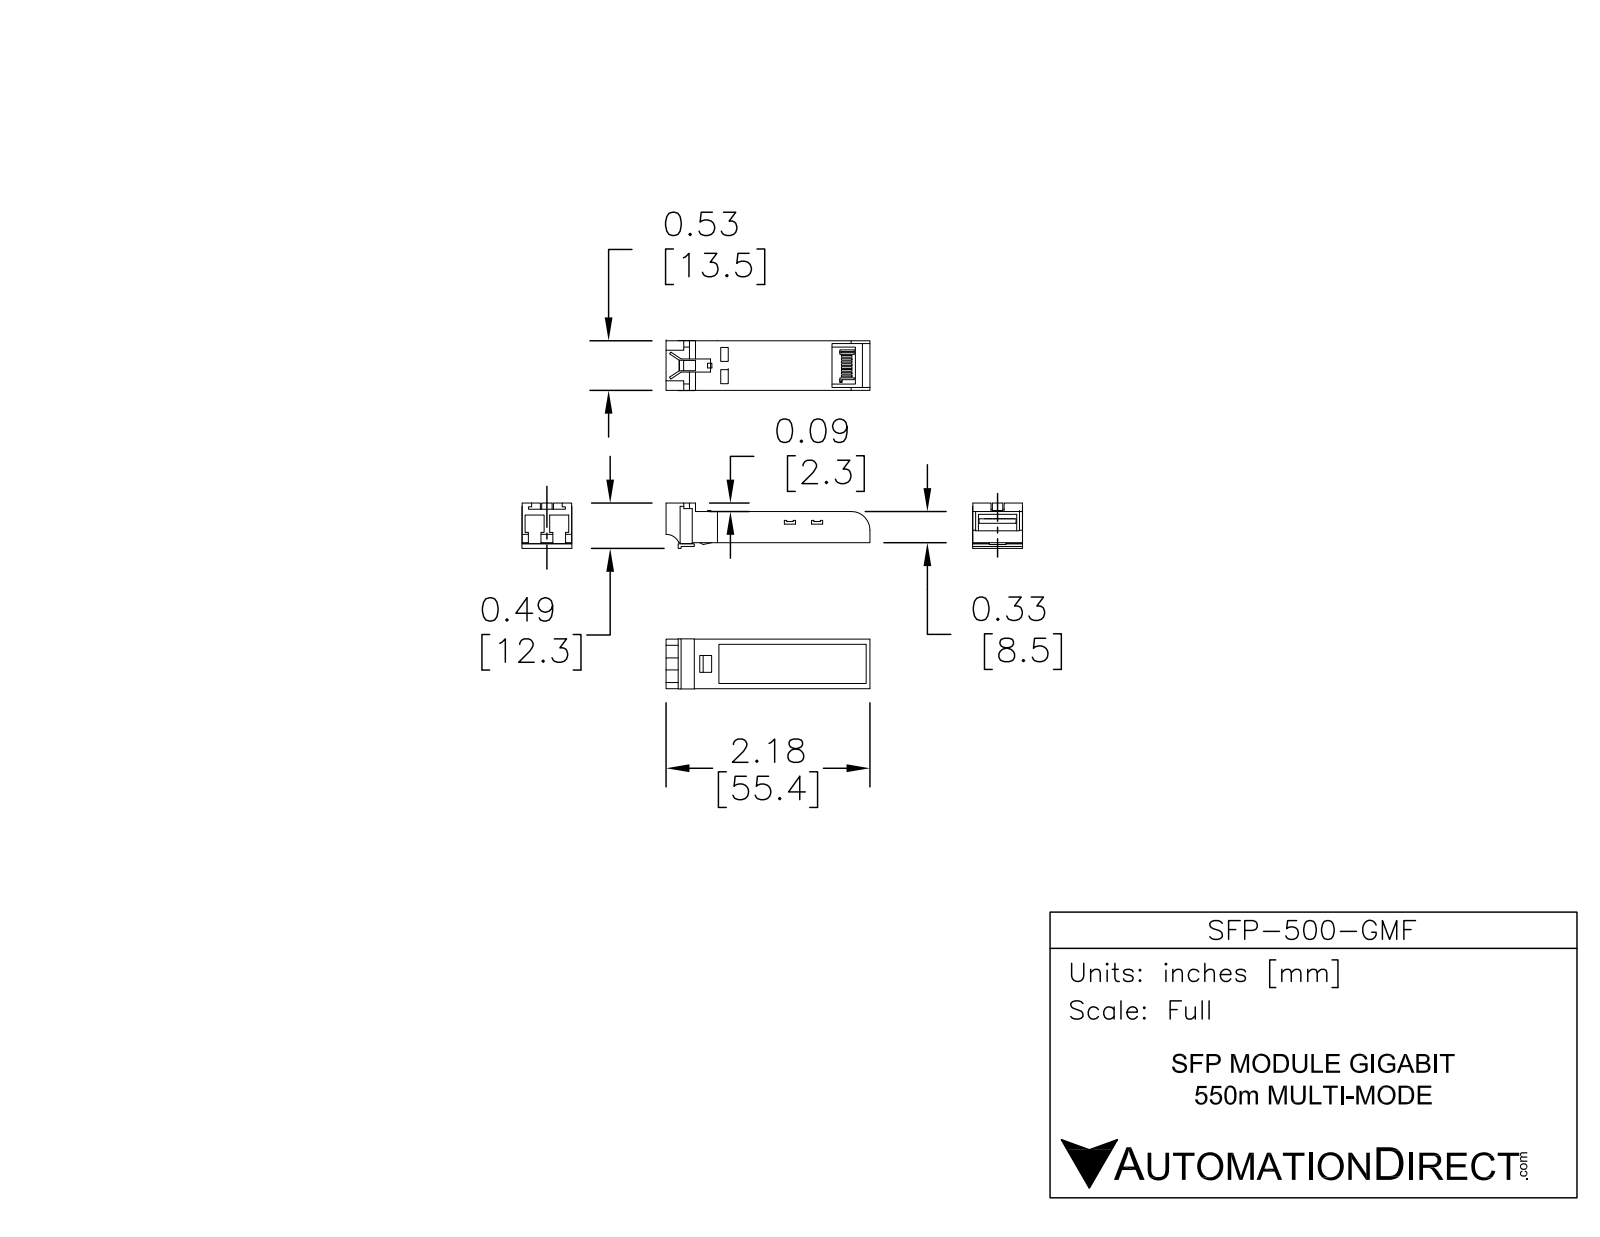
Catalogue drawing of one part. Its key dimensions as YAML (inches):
part_name: "SFP-500K-GMF"
step_written_by: "SolidWorks 2011 (AUTOMOTIVE_DESIGN)"
units: inches
bodies: {solids: 2, faces: 227, planar: 222, cylindrical: 5, other: 0}
overall_size: [2.18, 0.535, 0.485]
volume: 0.309
surface_area: 6.047
partial_cylinders:
  - {radius: 0.15, count: 1}
  - {radius: 0.2, count: 1}
face_to_face_distances: [0.53, 0.333, 0.03, 0.334, 0.5, 0.297, 0.034, 0.207, 0.256, 0.207]
